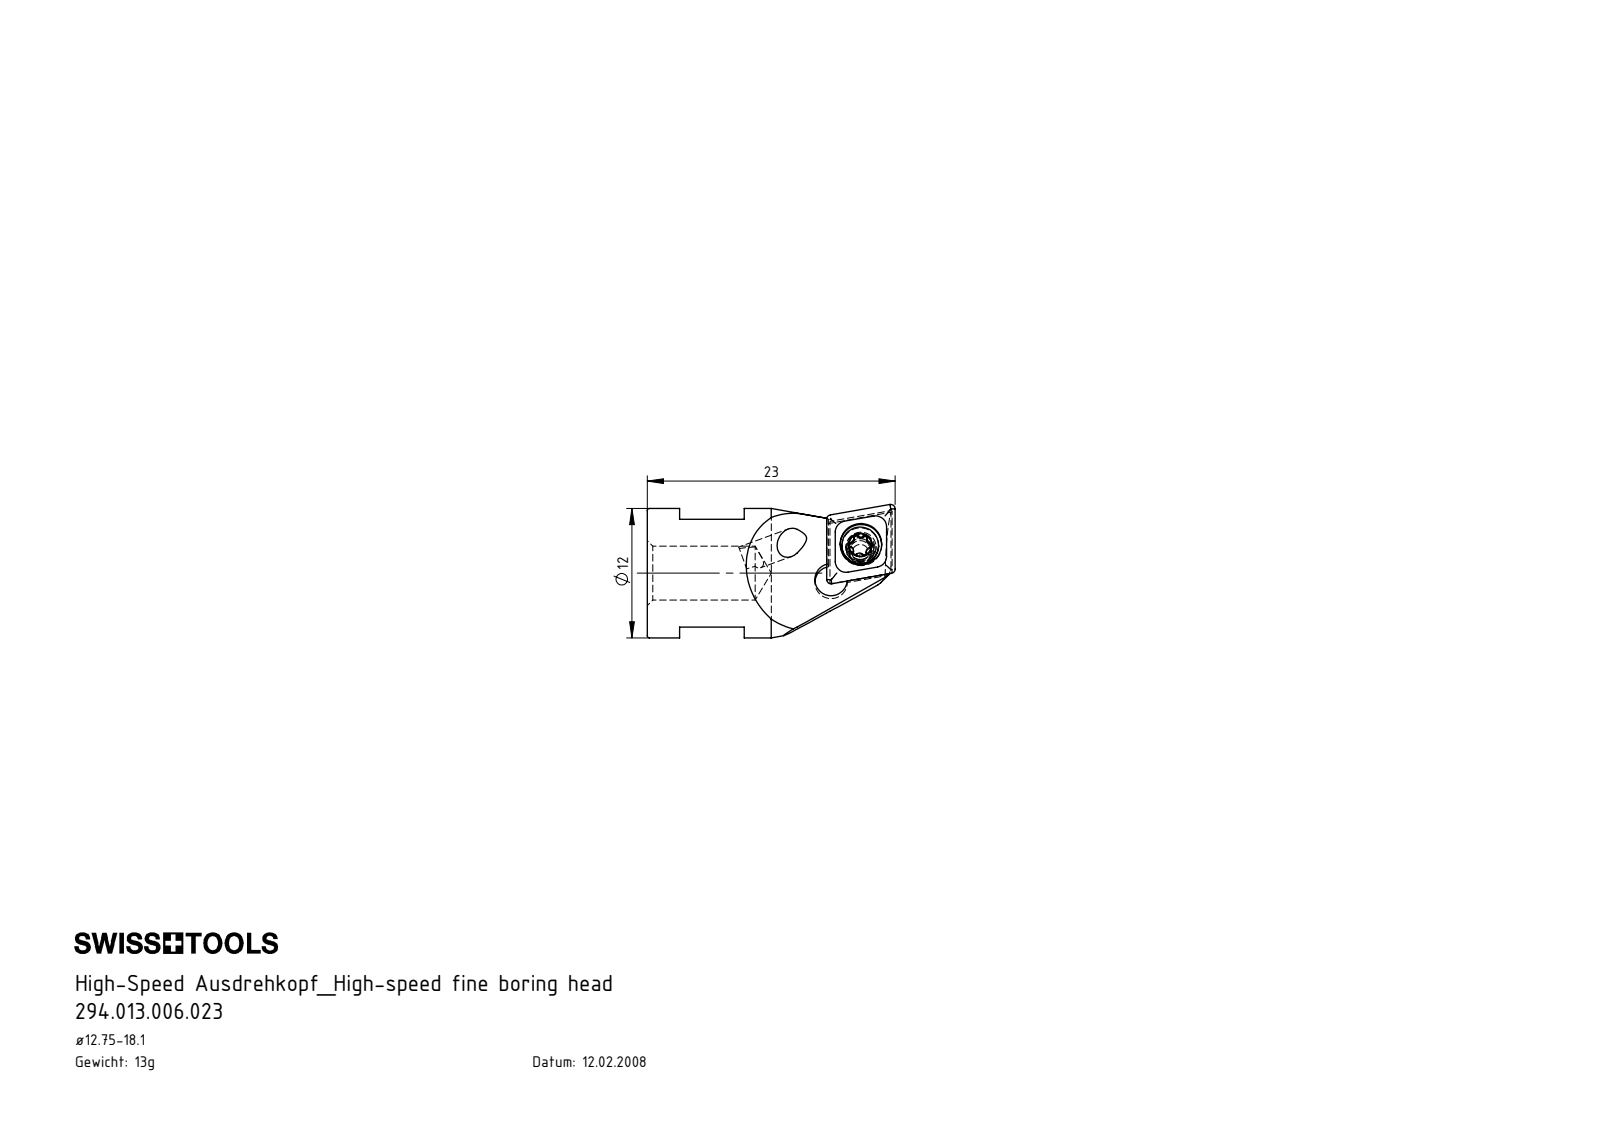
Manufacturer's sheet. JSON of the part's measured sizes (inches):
{"part_name": "CCMT060204; WCA-ER2.001.006_A; HS6-A13.K11.023_B; HS6.A13.K11.023", "step_written_by": "SolidWorks 2017 (AUTOMOTIVE_DESIGN)", "units": "inches", "bodies": {"solids": 3, "faces": 123, "planar": 34, "cylindrical": 35, "other": 54}, "overall_size": [0.906, 0.487, 0.473], "volume_in3": 0.095, "surface_area_in2": 2.04, "round_holes": [[0.081, 1], [0.098, 1], [0.11, 1], [0.152, 1], [0.197, 1]], "round_bosses_or_shafts": [[0.472, 1], [0.134, 1], [0.098, 1]], "partial_cylinders_radius": [[0.008, 6], [0.014, 5], [0.014, 1], [0.055, 1], [0.059, 1], [0.079, 1]], "face_to_face_distances": [0.394, 0.09, 0.236, 0.094, 0.354, 0.118, 0.661, 0.543, 0.307, 0.058]}
